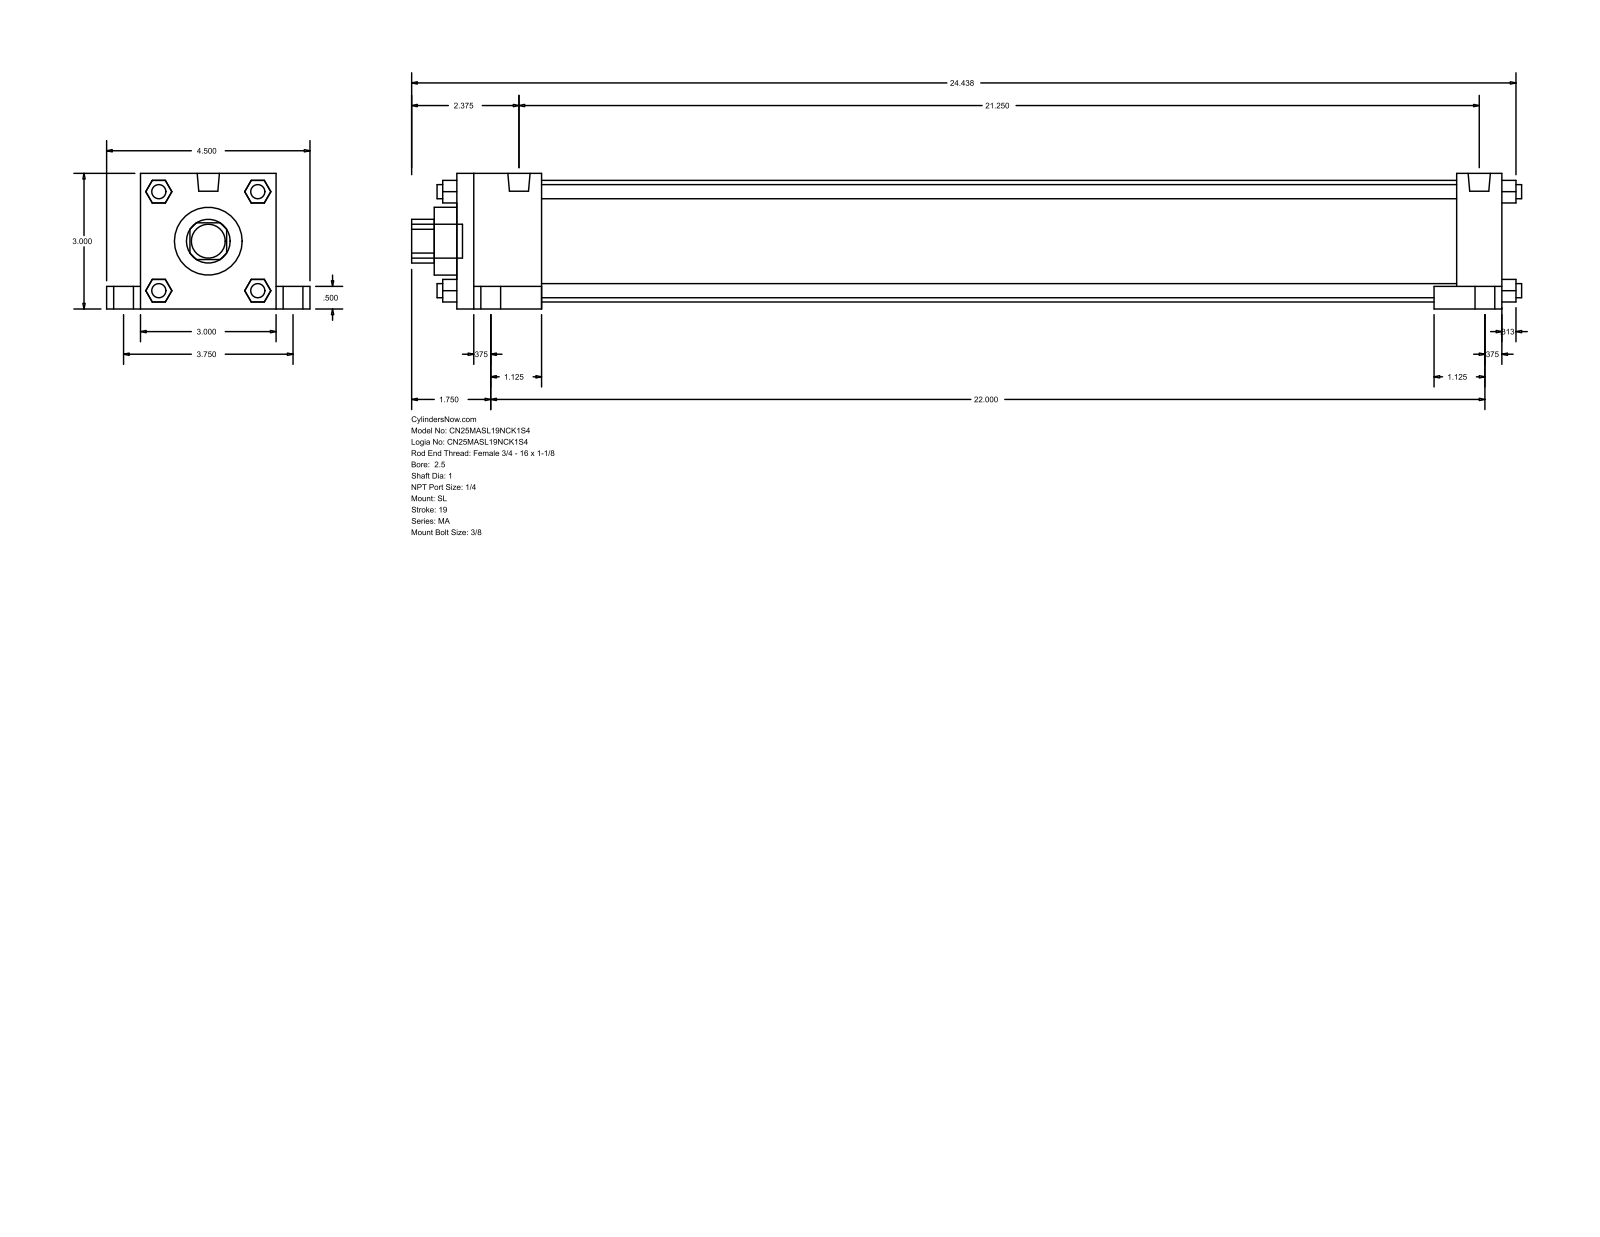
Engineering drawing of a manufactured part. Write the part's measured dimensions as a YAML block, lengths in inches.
part_name: "MA_SL__0250_1"
step_written_by: "GSSL Pune (CONFIG_CONTROL_DESIGN)"
units: inches
bodies: {solids: 0, faces: 148, planar: 112, cylindrical: 36, other: 0}
overall_size: [24.563, 4.5, 3]
round_holes:
  - {diameter: 1, count: 1}
  - {diameter: 1.5, count: 1}
  - {diameter: 2.69, count: 1}
round_bosses_or_shafts:
  - {diameter: 0.313, count: 8}
  - {diameter: 0.687, count: 4}
  - {diameter: 0.437, count: 4}
  - {diameter: 0.492, count: 2}
  - {diameter: 0.75, count: 1}
partial_cylinders:
  - {radius: 0.484, count: 1}
face_to_face_distances: [3, 23.125, 0.5, 20.25, 1, 1.875, 21.25, 22.125, 0.75, 3.75]
